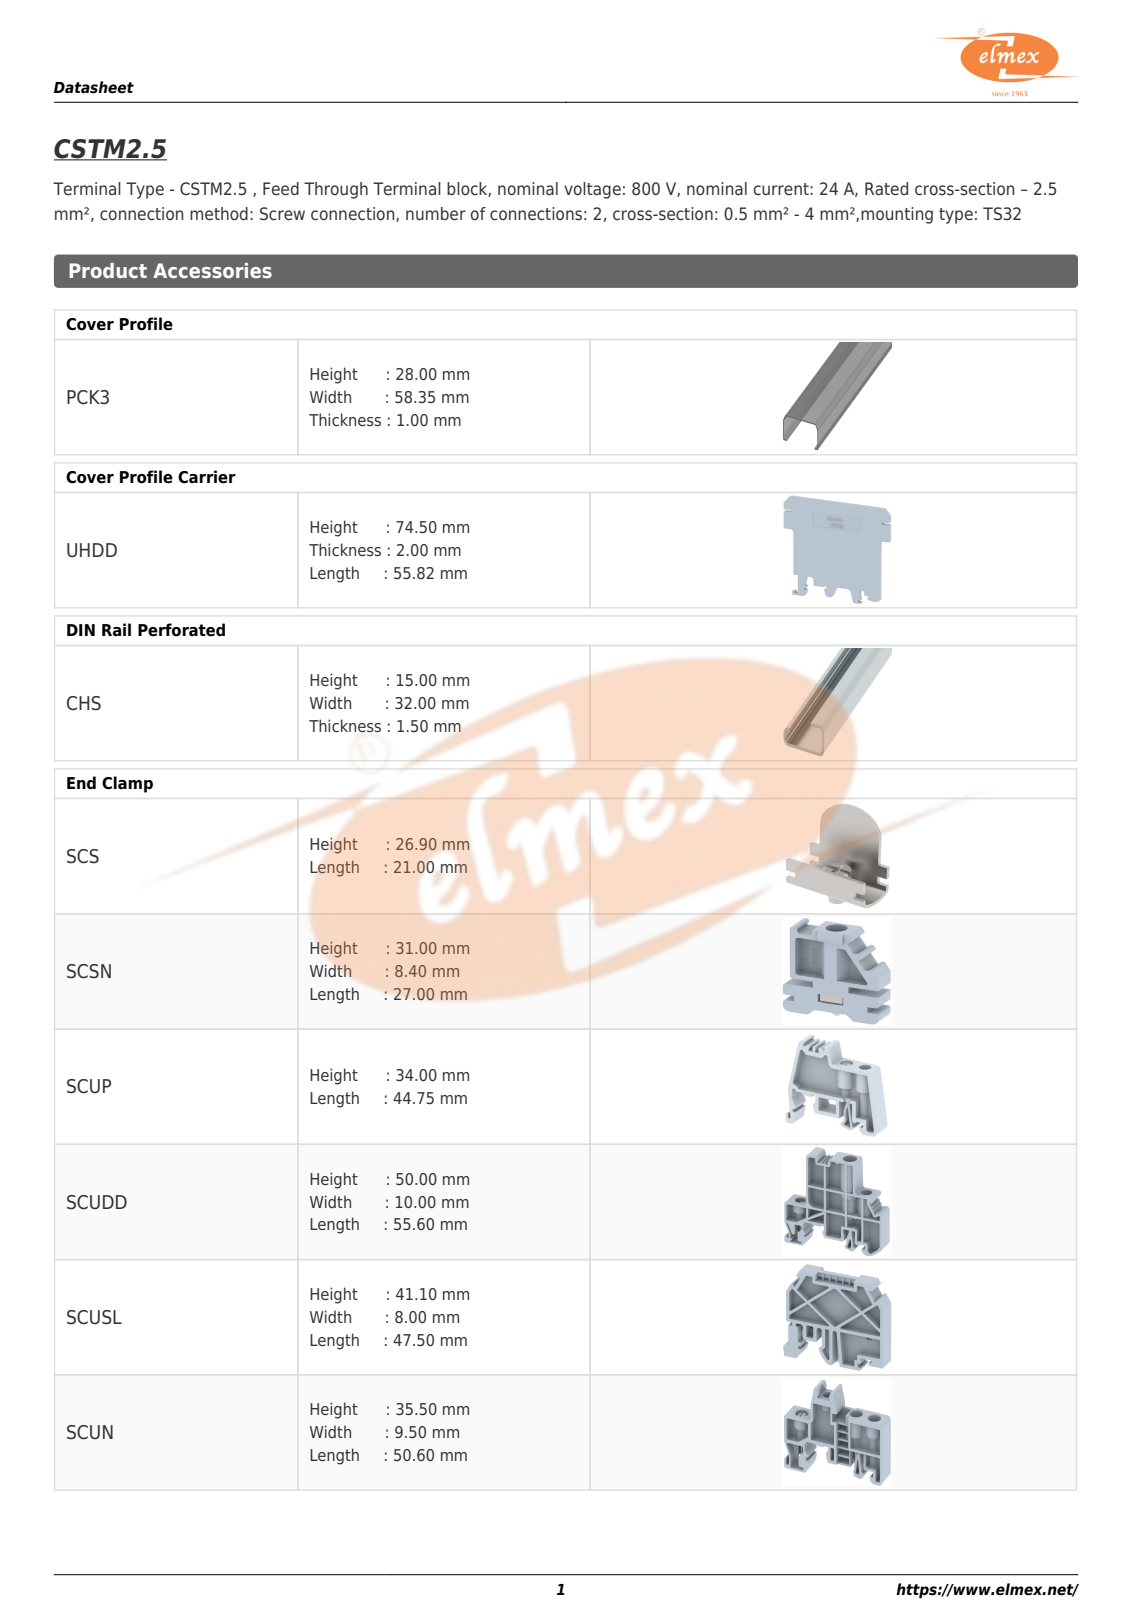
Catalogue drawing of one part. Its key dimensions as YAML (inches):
part_name: "6CSTM2.5_CO"
step_written_by: "ST-DEVELOPER v16 (AUTOMOTIVE_DESIGN)"
units: inches
bodies: {solids: 1, faces: 19, planar: 16, cylindrical: 3, other: 0}
overall_size: [1.732, 1.437, 0.236]
volume: 0.496
surface_area: 5.648
partial_cylinders:
  - {radius: 0.059, count: 2}
  - {radius: 0.051, count: 1}
face_to_face_distances: [0.236, 1.437, 1.732, 0.523, 0.914, 0.492, 1.24, 0.541, 0.049, 1.191]
